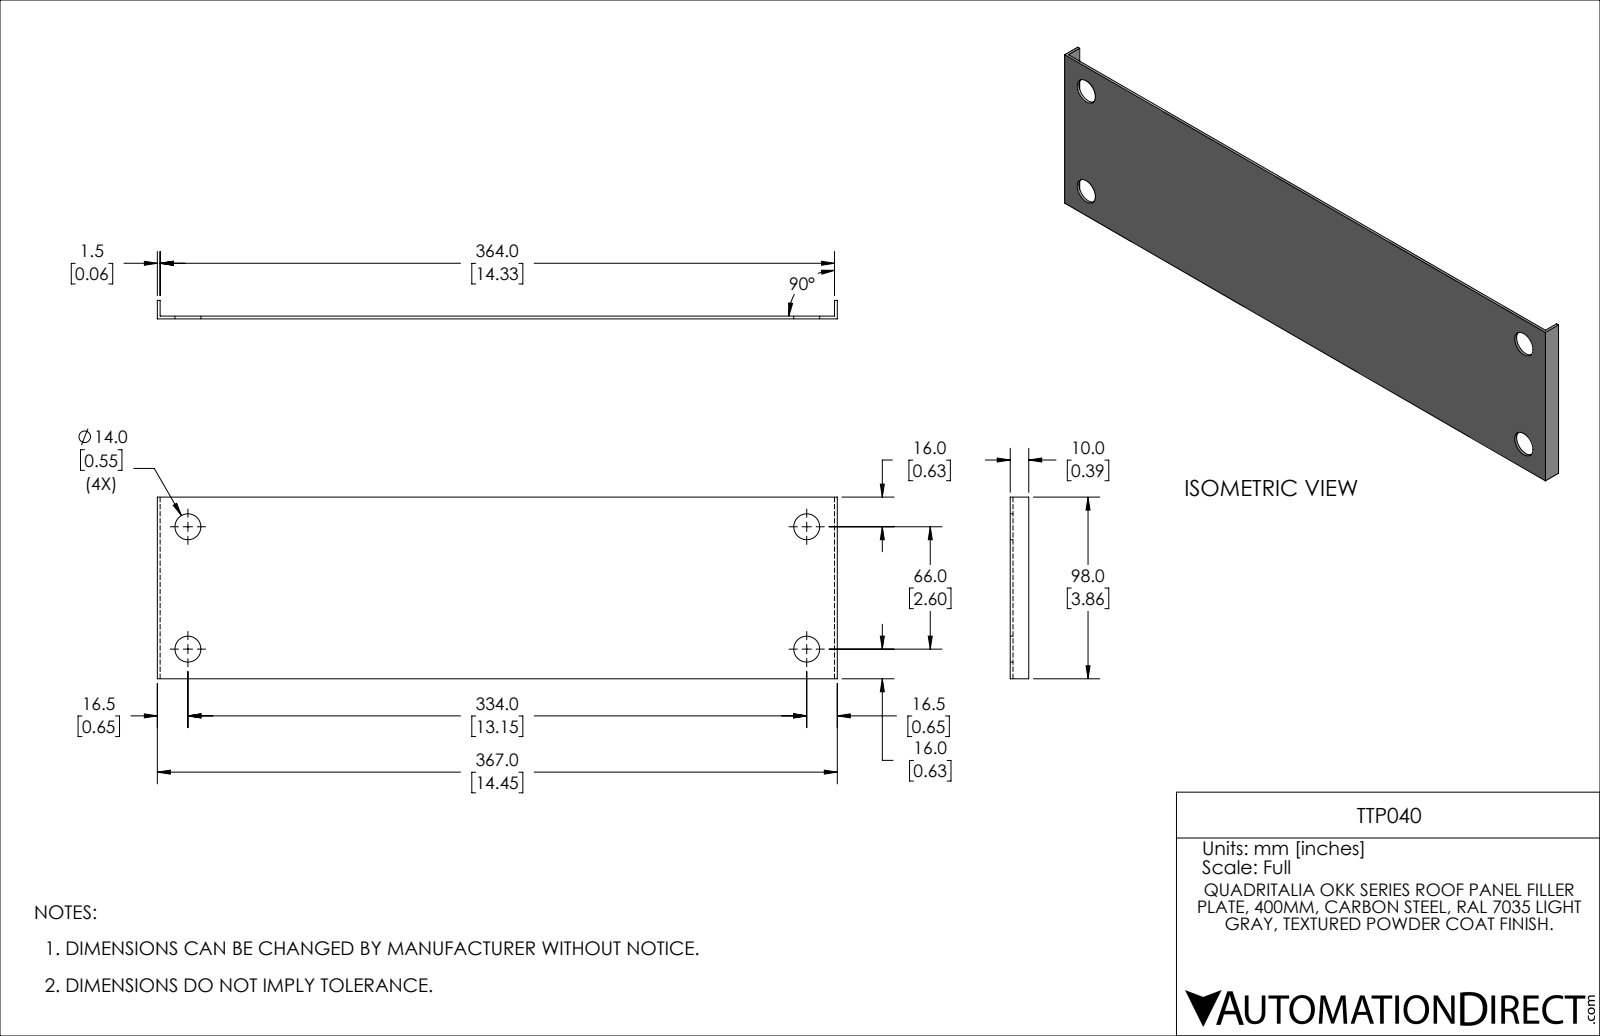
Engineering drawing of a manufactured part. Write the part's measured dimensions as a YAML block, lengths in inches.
part_name: "TTP040"
step_written_by: "SolidWorks 2021 (CONFIG_CONTROL_DESIGN)"
units: inches
bodies: {solids: 1, faces: 14, planar: 10, cylindrical: 4, other: 0}
overall_size: [14.449, 3.858, 0.394]
volume: 3.388
surface_area: 117.4
round_holes:
  - {diameter: 0.551, count: 4}
face_to_face_distances: [0.059, 14.39, 14.449, 14.331, 3.858, 0.335, 0.394]
hole_center_spacings: [2.598, 13.15, 13.404]
